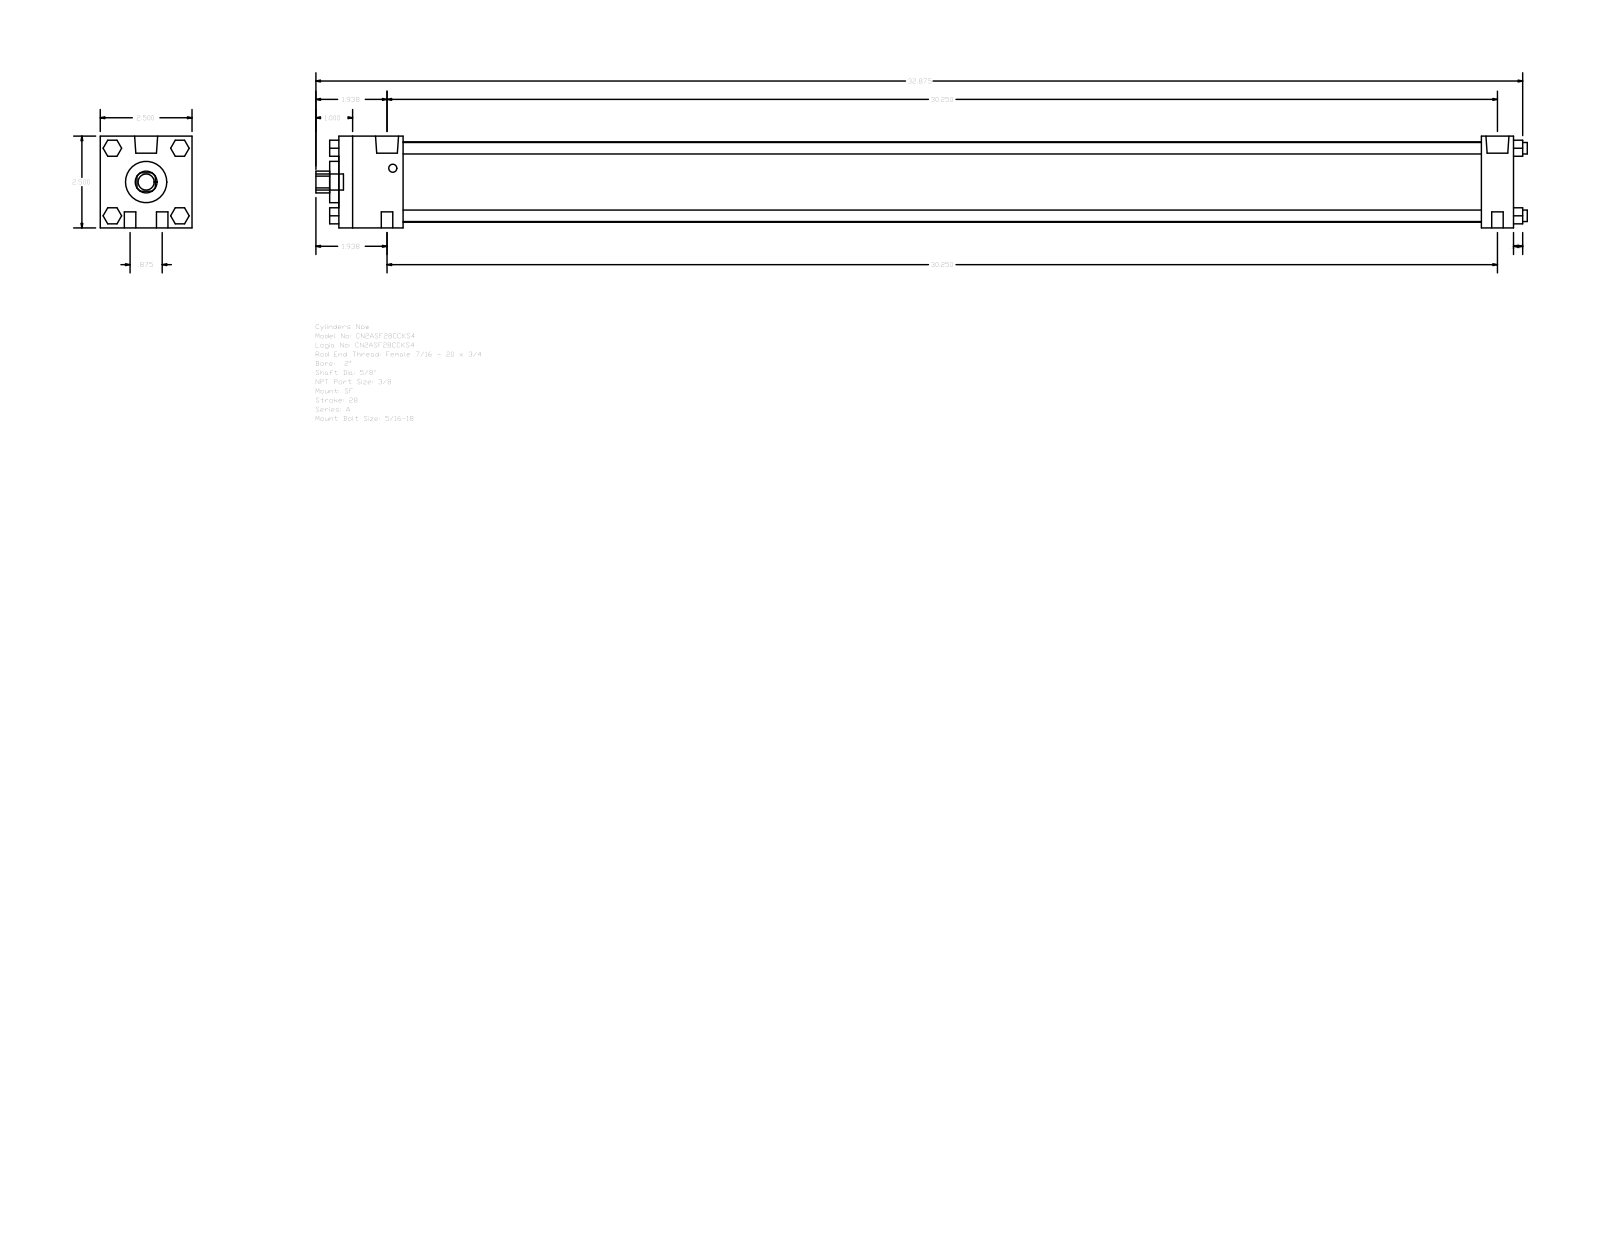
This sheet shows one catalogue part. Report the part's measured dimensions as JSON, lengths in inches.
{"part_name": "A_SF__0200_0.625", "step_written_by": "GSSL Pune (CONFIG_CONTROL_DESIGN)", "units": "inches", "bodies": {"solids": 0, "faces": 124, "planar": 94, "cylindrical": 30, "other": 0}, "overall_size": [33, 2.5, 2.5], "round_holes": [[0.625, 1], [1.125, 1], [2.19, 1]], "round_bosses_or_shafts": [[0.313, 8], [0.627, 2], [0.219, 2], [0.437, 1]], "partial_cylinders_radius": [[0.297, 1]], "face_to_face_distances": [2.5, 32, 31.125, 0.875, 1.75, 29.375, 30.25, 0.25, 32.25, 2]}
